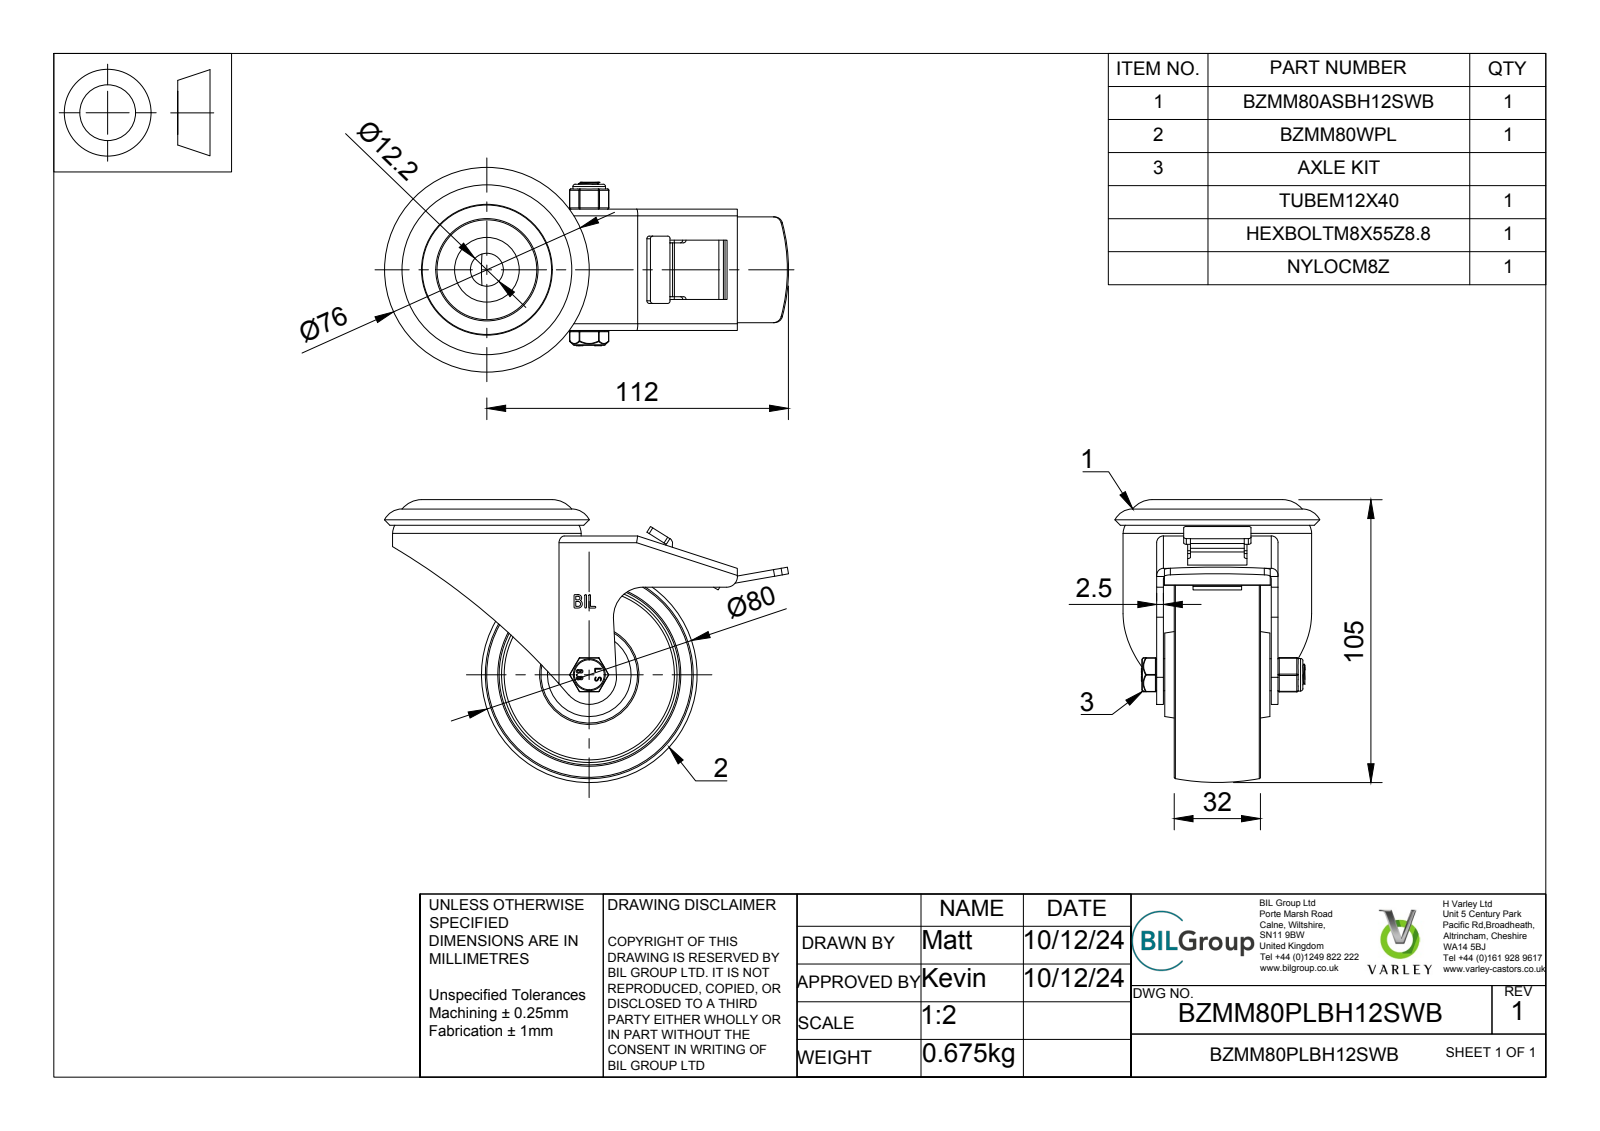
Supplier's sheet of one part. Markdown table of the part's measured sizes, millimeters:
| quantity | value |
| --- | --- |
| part name | BZMM80PLBH12SWB v3; BZMM80ASBH12SWB v1; ZINC PLATED, PRESSED STEEL HEAD; ZINC PLATED, PRESSED STEEL FORKS (+8 more) |
| STEP written by | Autodesk Translation Framework v13.20.0.188 (AP242_MANAGED_MODEL_BASED_3D_ENGINEERING_MIM_LF) |
| units | millimeters |
| bodies | 9 solids, 589 faces (275 planar, 208 cylindrical, 106 other) |
| overall size | 150 × 105 × 76 |
| volume | 167 259 mm³ |
| surface area | 87 645 mm² |
| round holes (diameter × count) | 0.66 × 2, 12.2 × 2, 8 × 1, 8.2 × 1, 8.4 × 1, 8.6 × 1, 65 × 1, 72 × 1 |
| round bosses / shafts (diameter × count) | 70 × 1, 49.5 × 1, 38 × 1, 24 × 1, 21.31 × 1, 12.1 × 1, 11.9 × 1, 11.5 × 1 |
| partial cylindrical surfaces (radius × count) | 0.75 × 48, 0.5 × 26, 0.25 × 12, 1 × 6, 1.25 × 6, 2 × 5, 2.5 × 5, 0.33 × 4 |
| main face-to-face distances | 2.5, 19, 26, 16.5, 23.5, 42.5, 7, 12.5, 6.5, 4 |
| hole center spacings | 3.22, 2.49 |
